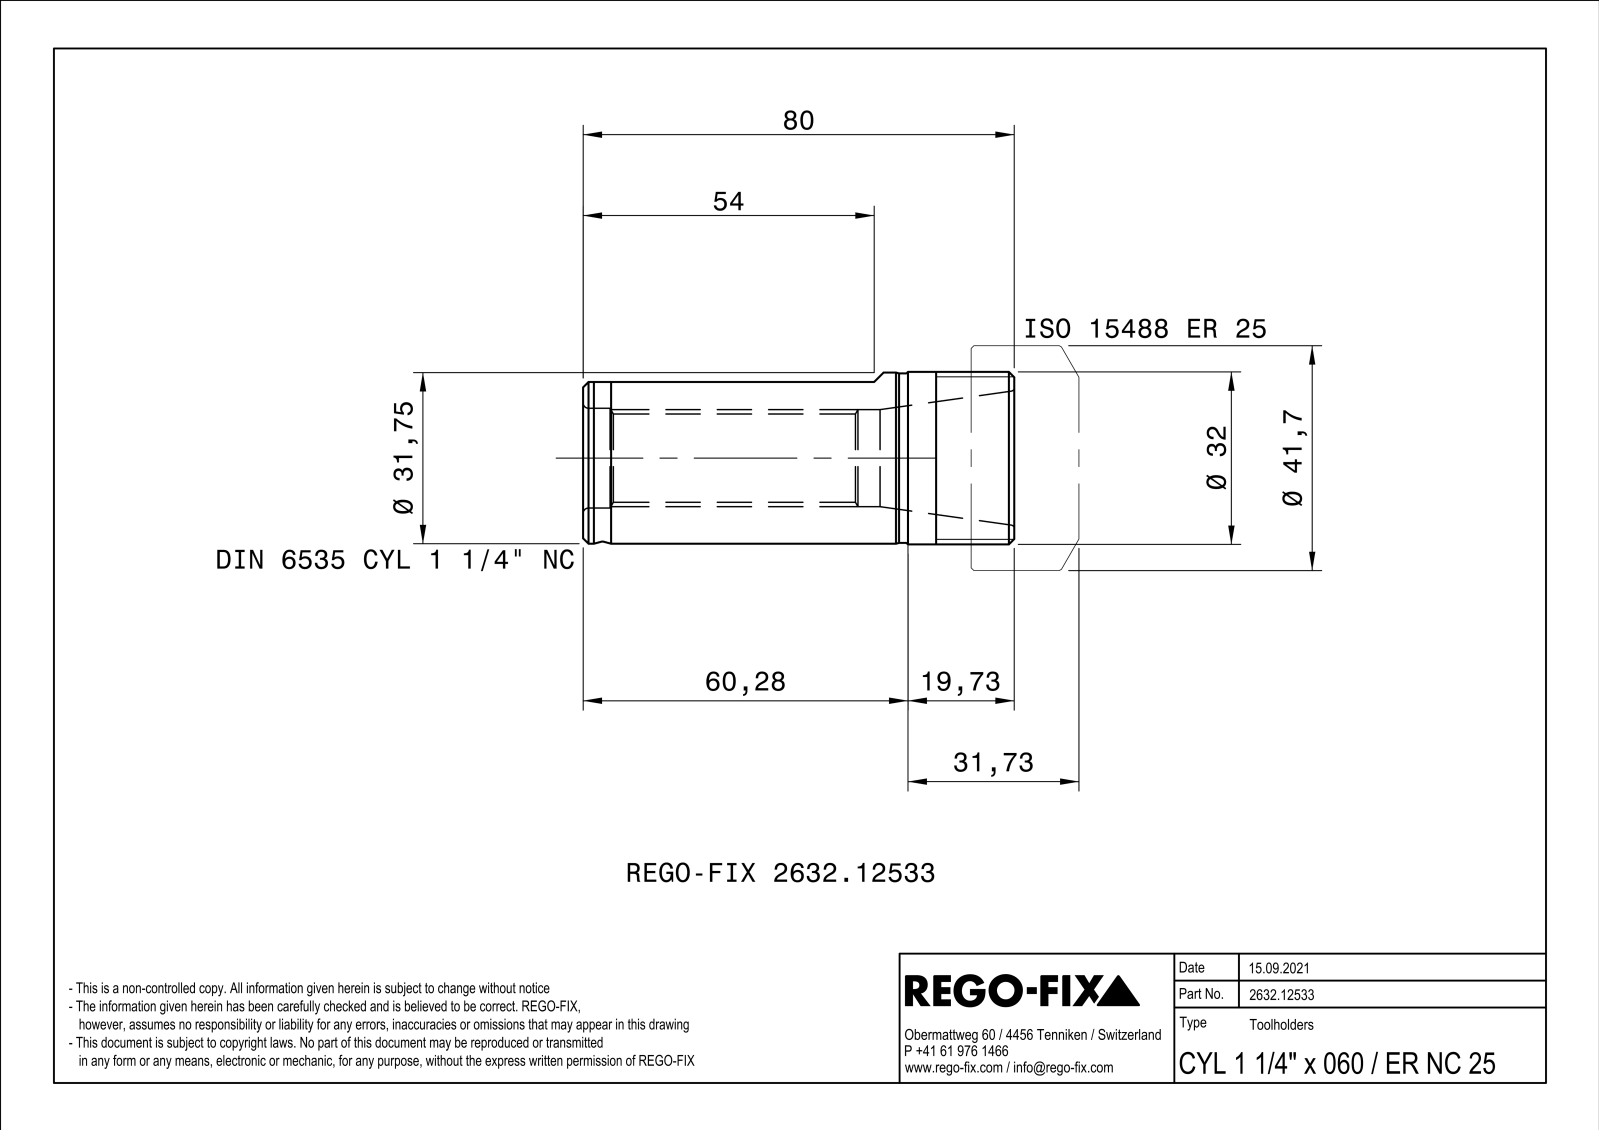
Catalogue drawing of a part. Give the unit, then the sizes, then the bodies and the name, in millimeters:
Units: millimetres
Overall size (bounding box): 80 × 32 × 32
Round holes (diameter × count): ⌀16.38 ×1, ⌀18 ×1, ⌀18.5 ×1
Round bosses / shafts (diameter × count): ⌀32 ×1, ⌀31.75 ×1, ⌀31.45 ×1
Main face-to-face distances: 80, 37.47
Volume: 41 229 mm³ · Surface area: 13 298 mm²
Bodies: 1 solid, 26 faces (5 planar, 8 cylindrical, 13 other)
Part name (STEP PRODUCT): NOCUT
STEP written by: SIEMENS PLM Software Solid Edge ST10 (AUTOMOTIVE_DESIGN)
